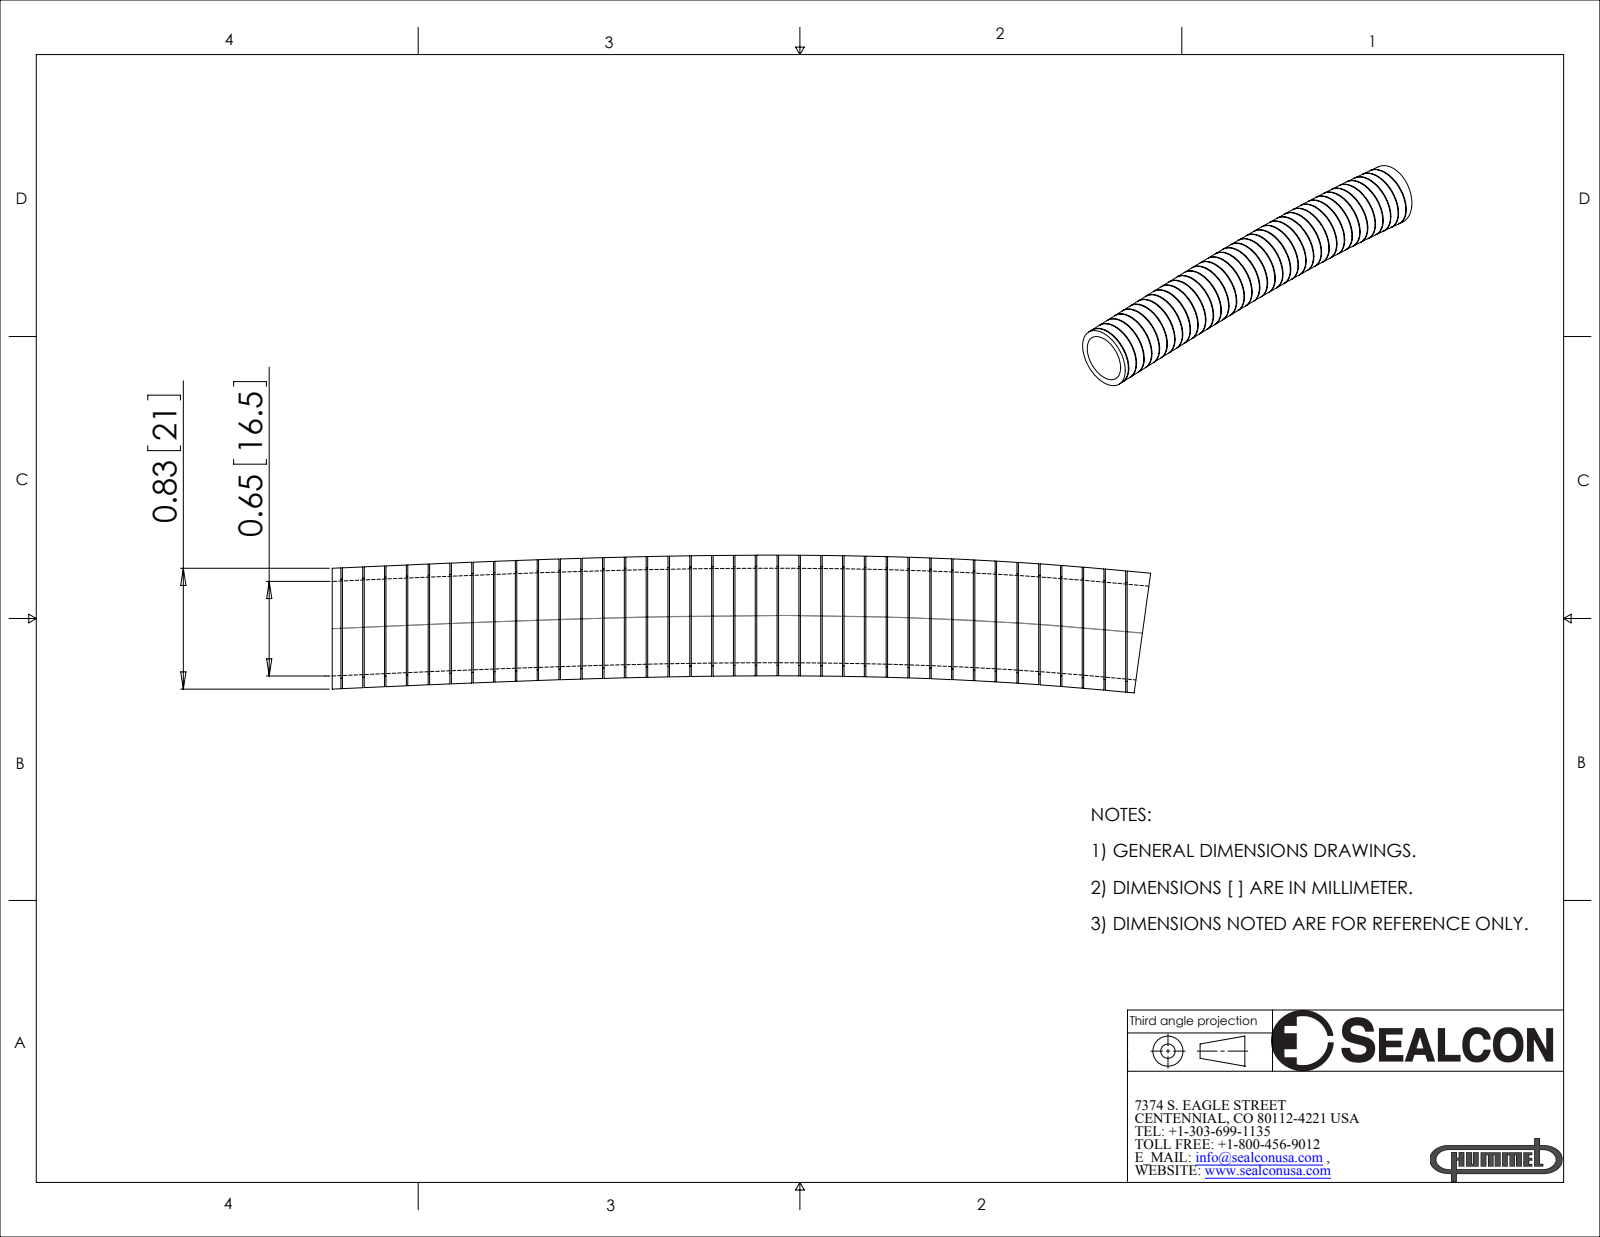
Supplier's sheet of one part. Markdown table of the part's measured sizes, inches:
| quantity | value |
| --- | --- |
| part name | SM-1013-HY |
| STEP written by | SolidWorks 2007 (AUTOMOTIVE_DESIGN) |
| units | inches |
| bodies | 1 solid, 228 faces (76 planar, 74 cylindrical, 78 other) |
| overall size | 5.627 × 0.946 × 0.83 |
| volume | 1.1 in³ |
| surface area | 39.32 in² |
| round bosses / shafts (diameter × count) | 0.68 × 35 |
| main face-to-face distances | 0.15, 0.299, 0.159, 0.14, 0.449, 0.299, 0.448, 0.309, 0.598, 0.289 |
